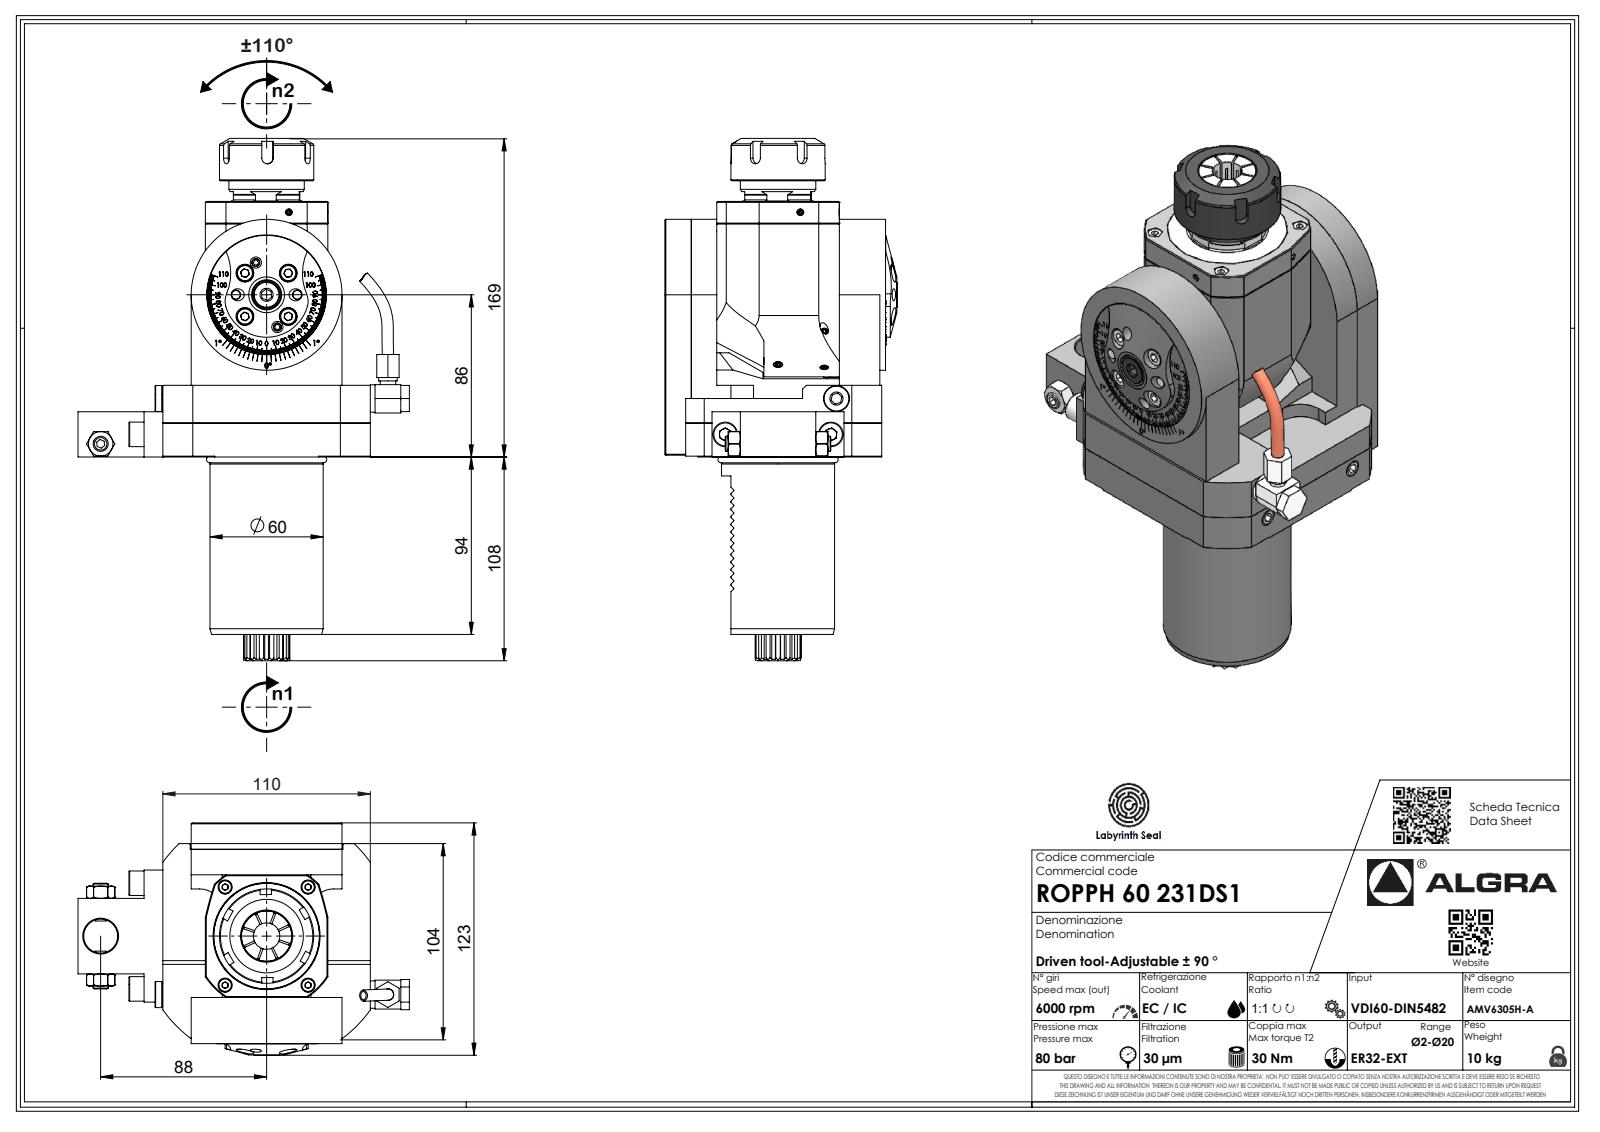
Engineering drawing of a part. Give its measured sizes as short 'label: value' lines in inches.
name: ROPPH60231DS1
written by: SolidWorks 2023 (AUTOMOTIVE_DESIGN)
unit: in
bodies: 1 solid, 693 faces (425 planar, 127 cylindrical, 141 other)
size: 10.902 × 6.917 × 4.843
volume: 90.56 in³; area: 196.7 in²
holes: 1× ⌀0.083, 1× ⌀0.197
bosses: 1× ⌀3.15, 1× ⌀2.362, 1× ⌀2.311, 1× ⌀1.969, 1× ⌀1.575, 1× ⌀0.571, 1× ⌀0.386, 1× ⌀0.323
rounds: 14× R0.012, 7× R0.013, 7× R0.02, 7× R0.146, 5× R0.118, 3× R0.008, 2× R0.394, 2× R0.472
face distances: 0.886, 3.445, 2.559, 3.15, 0.295, 3.74, 5.335, 0.276, 1.083, 3.701
